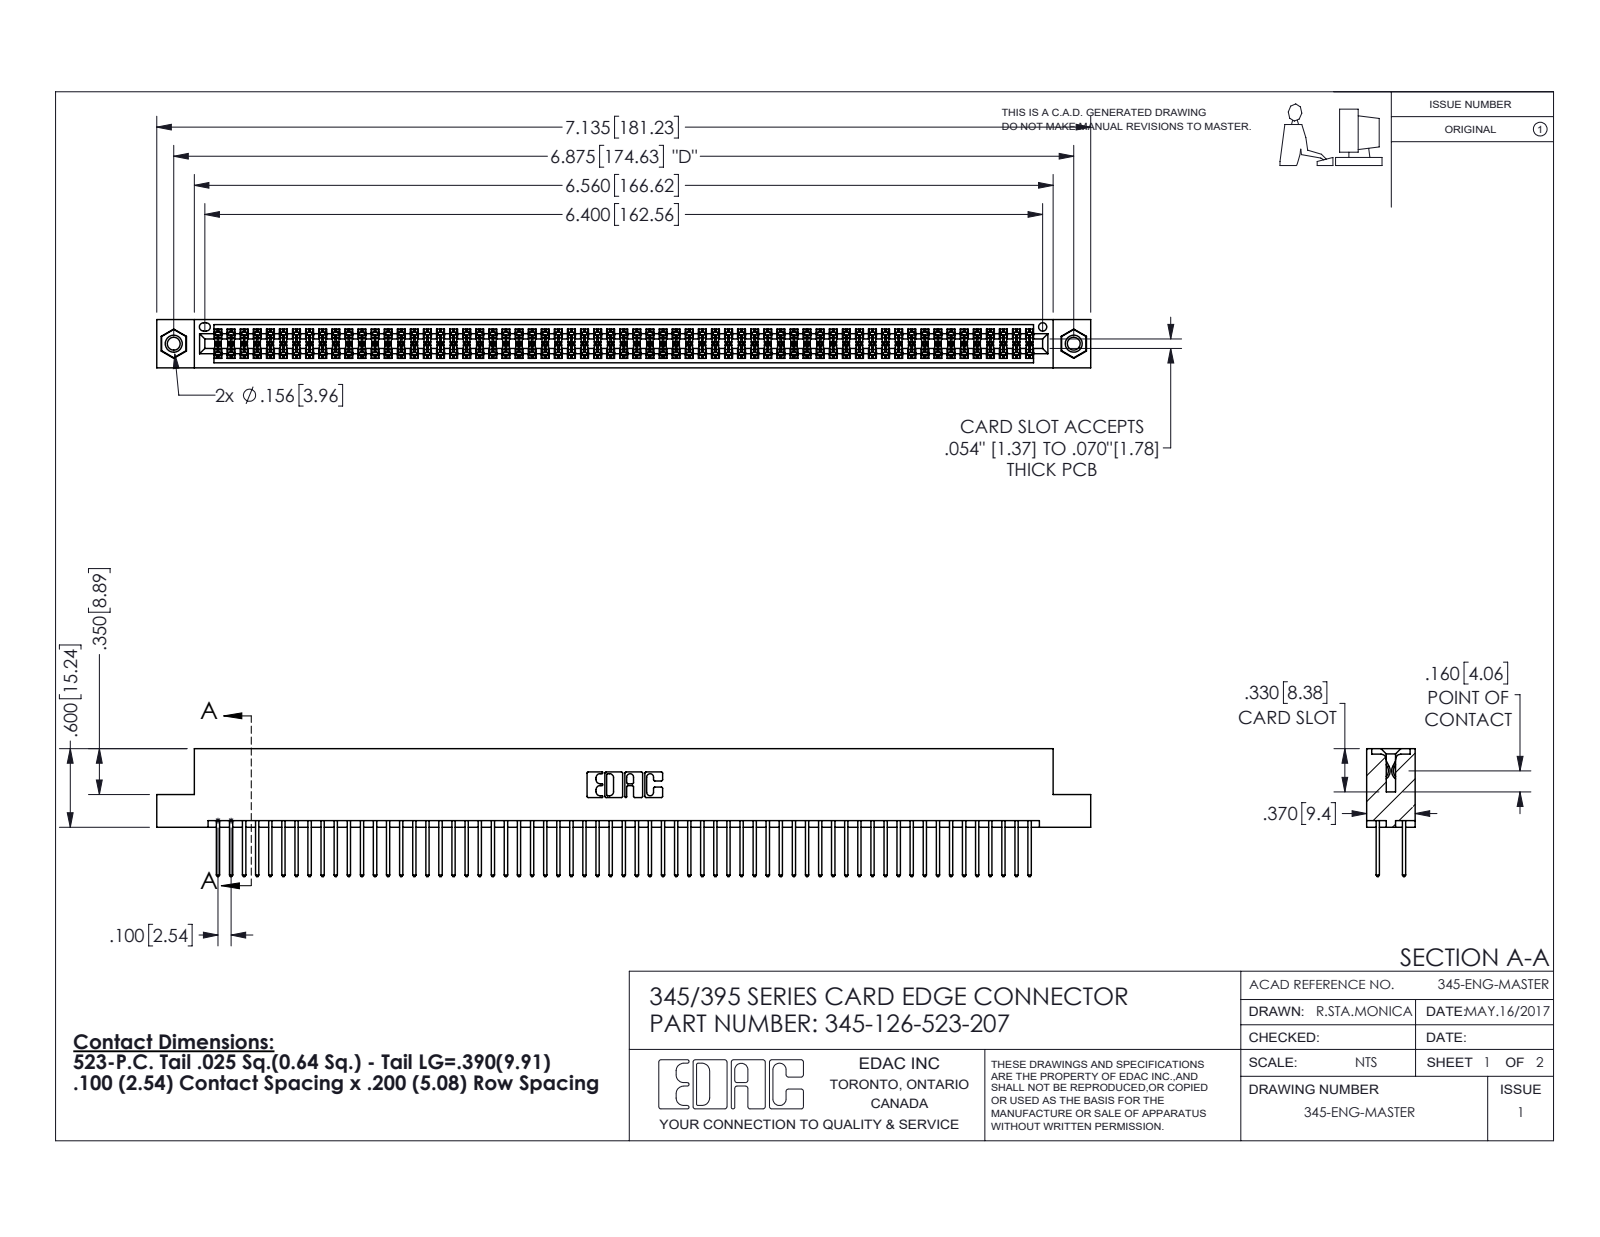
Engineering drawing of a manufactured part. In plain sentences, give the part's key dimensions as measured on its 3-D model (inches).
The part is named "345-292-001_345-293-123; 345 Part_Flush Mounting Lugs - 0.156 Dia-TI; 345-250-001_345-250-005-103; 345-126-523-207". Its 3-D file was written by "SolidWorks 2016 (CONFIG_CONTROL_DESIGN)". It is 129 solids with 6486 faces: 4270 planar, 2200 cylindrical and 16 other. Overall it measures 7.135 by 0.977 by 0.37 inches. Its volume is 1.101 cubic inches and its surface area 43.81 square inches. Round holes: 2 of diameter 0.098, 2 of diameter 0.125, 2 of diameter 0.156, 1 of diameter 0.064. Round bosses or shafts: 2 of diameter 0.155. Partial cylindrical surfaces (rounded edges, fillets, slot ends): 189 of radius 0.006, 126 of radius 0.01, 22 of radius 0.01, 6 of radius 0.007, 6 of radius 0.031, 3 of radius 0.026, 2 of radius 0.014, 2 of radius 0.019. The main face-to-face distances are 0.072, 0.298, 0.2, 0.098, 0.272, 0.025, 0.37, 0.225, 0.175, 0.149. The hole center spacings are 0.27, 6.639, 6.875.
